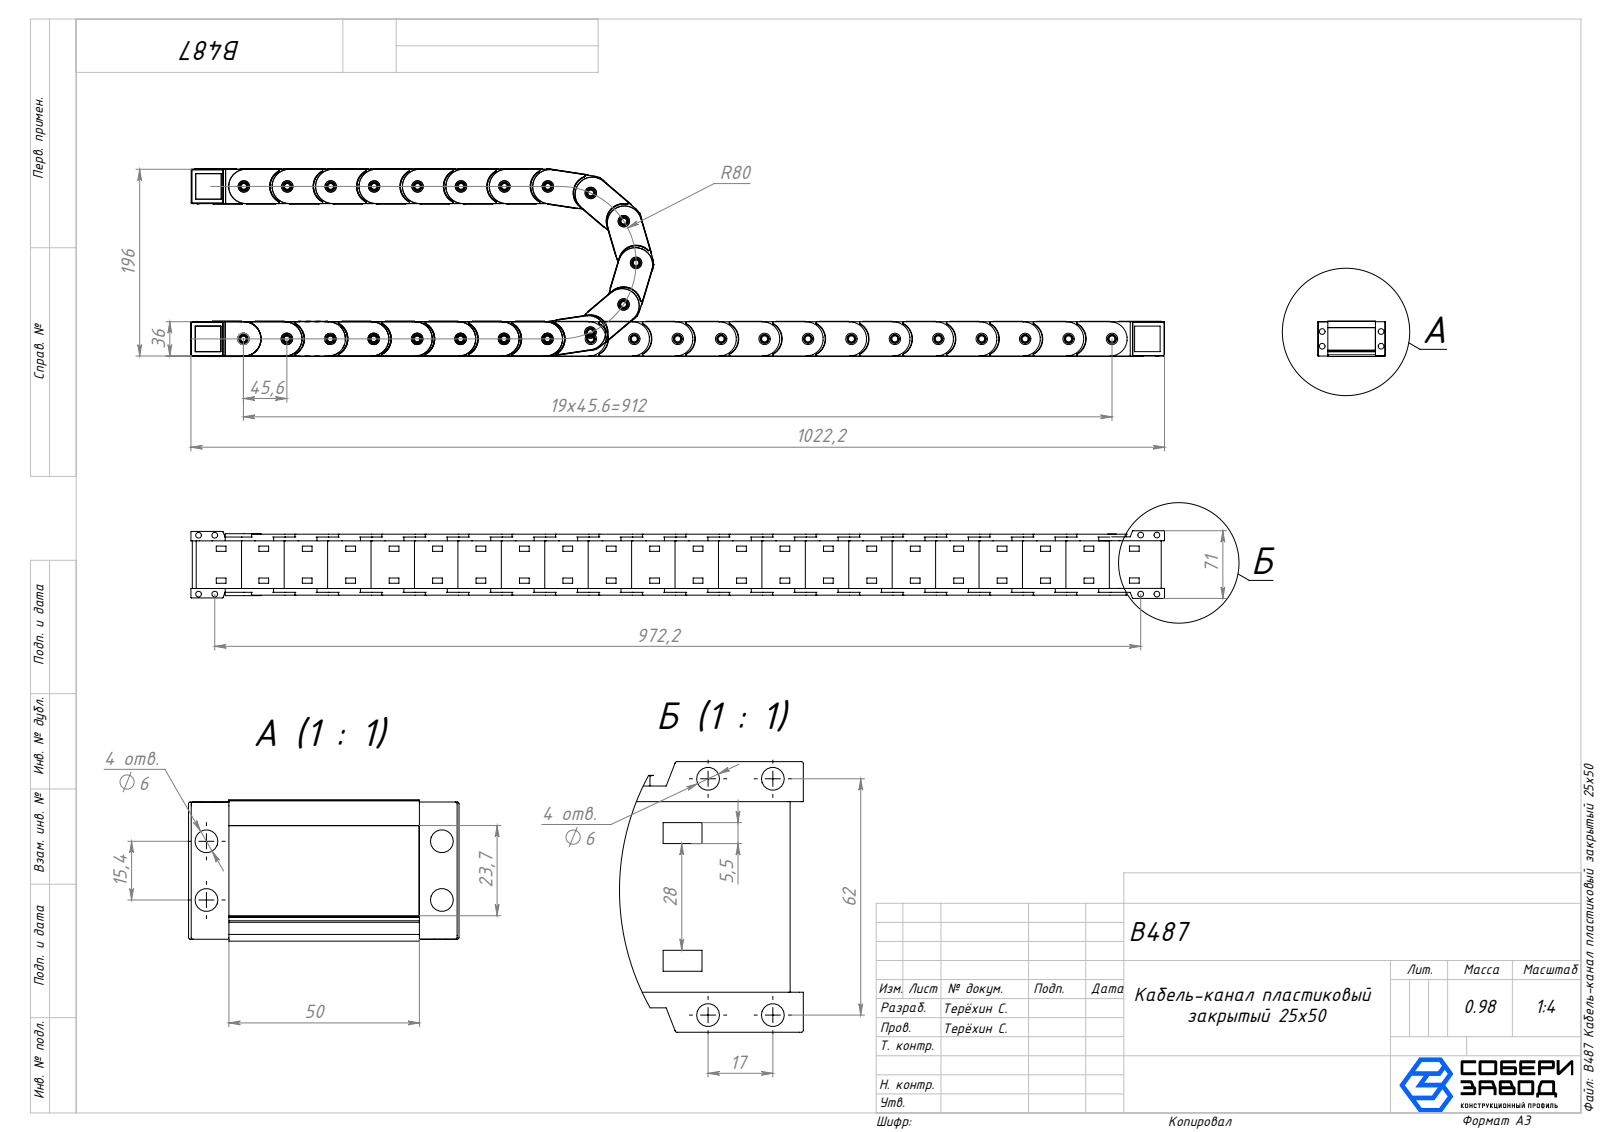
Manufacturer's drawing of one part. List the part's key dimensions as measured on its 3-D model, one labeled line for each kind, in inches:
Part name (STEP PRODUCT): СБ_конеч.звено_00; Крышка_короткая_00; СБ_нач.звено_00; Стенки для середины_00 (+5 more)
STEP written by: SolidWorks 2025 (AUTOMOTIVE_DESIGN)
Units: inches
Bodies: 90 solids, 5496 faces (3332 planar, 1780 cylindrical, 384 other)
Overall size (bounding box): 40.246 × 2.795 × 1.457
Volume: 48.12 in³ · Surface area: 969.6 in²
Round holes (diameter × count): ⌀0.248 ×22, ⌀0.472 ×21, ⌀0.236 ×16, ⌀0.246 ×1
Round bosses / shafts (diameter × count): ⌀0.362 ×21
Partial cylindrical surfaces — rounded edges, fillets, slot ends (radius × count): R0.02 ×336, R0.039 ×274, R0.051 ×92, R0.709 ×83, R0.059 ×44, R0.118 ×22, R0.523 ×22, R0.594 ×22
Main face-to-face distances: 0.157, 2.126, 0.118, 0.276, 2.244, 2.402, 0.071, 1.382, 2.283, 1.969
Hole centre spacings: 1.795, 3.591, 5.386, 7.181, 8.976, 10.772, 12.567, 14.362
